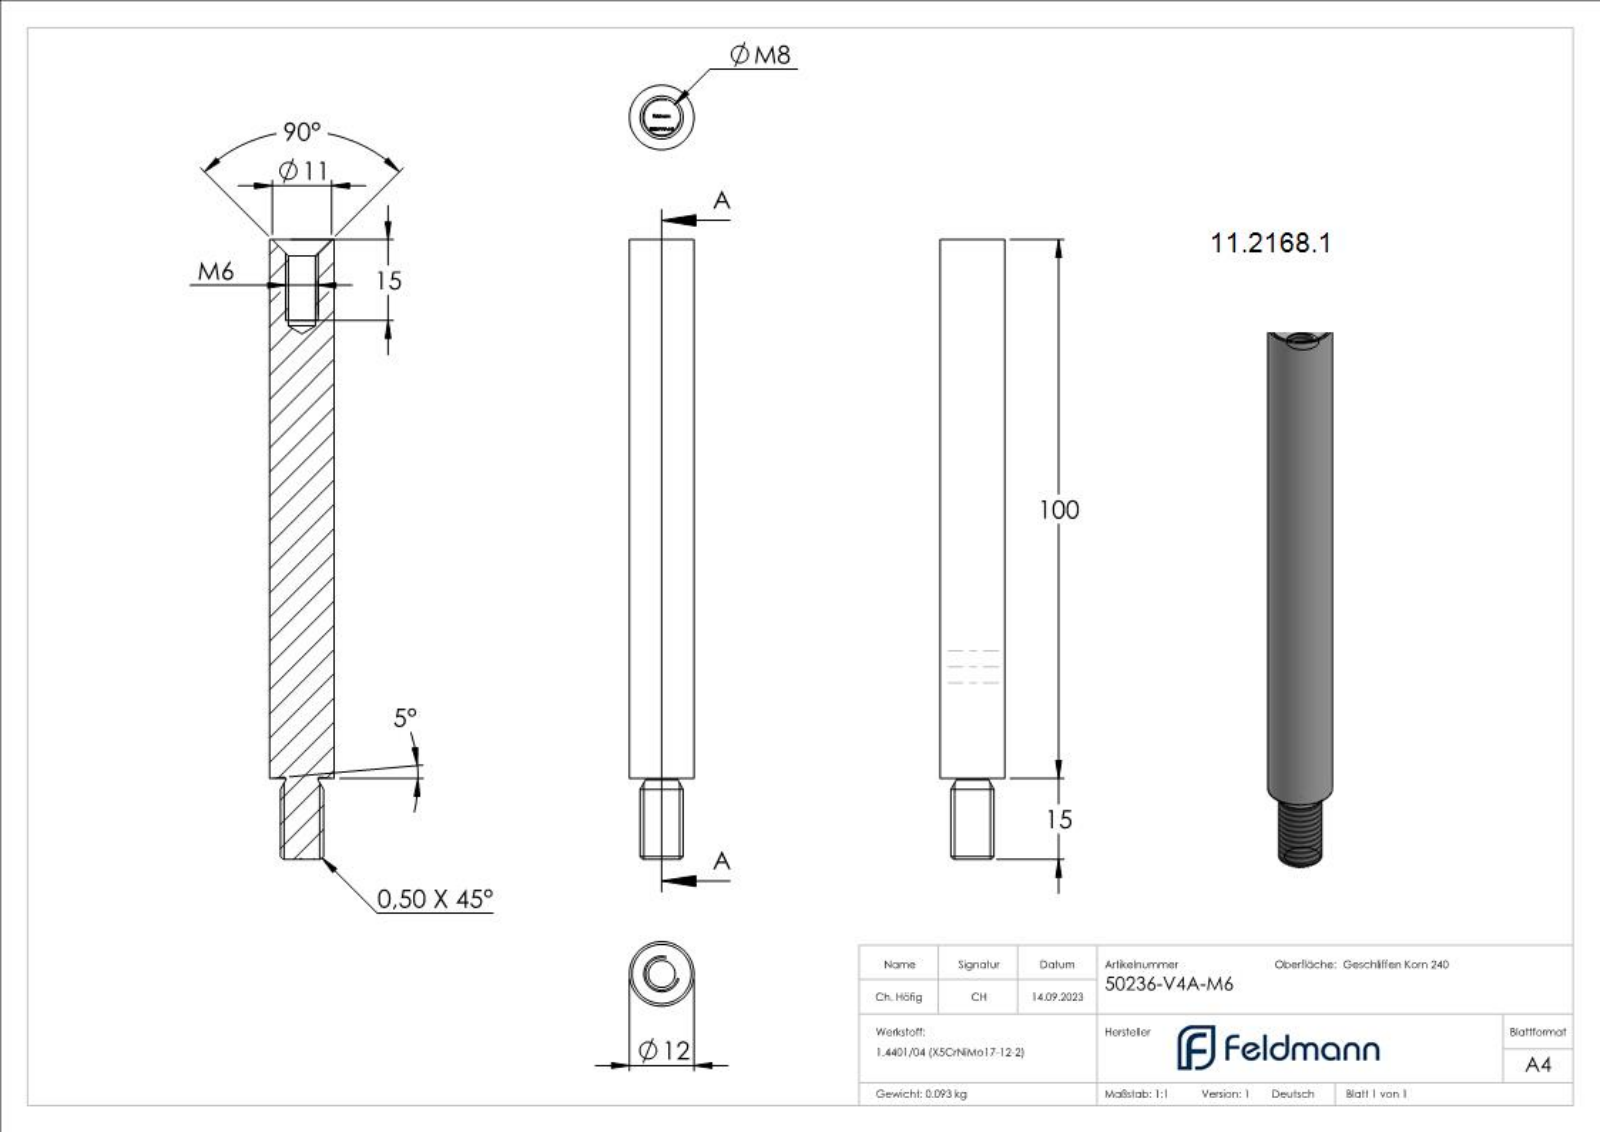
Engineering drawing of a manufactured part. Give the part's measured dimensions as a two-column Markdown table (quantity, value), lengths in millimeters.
| quantity | value |
| --- | --- |
| part name | 50236-V4A-M6 |
| STEP written by | SolidWorks 2018 (CONFIG_CONTROL_DESIGN) |
| units | millimeters |
| bodies | 1 solid, 269 faces (157 planar, 3 cylindrical, 109 other) |
| overall size | 115 × 12 × 12 |
| volume | 11 602 mm³ |
| surface area | 4 632 mm² |
| round holes (diameter × count) | 5 × 1 |
| round bosses / shafts (diameter × count) | 12 × 1, 8 × 1 |
| main face-to-face distances | 115, 114.9, 0.77, 1.29, 2.38, 2.39, 0.72, 1.55, 2.44, 0.57 |
